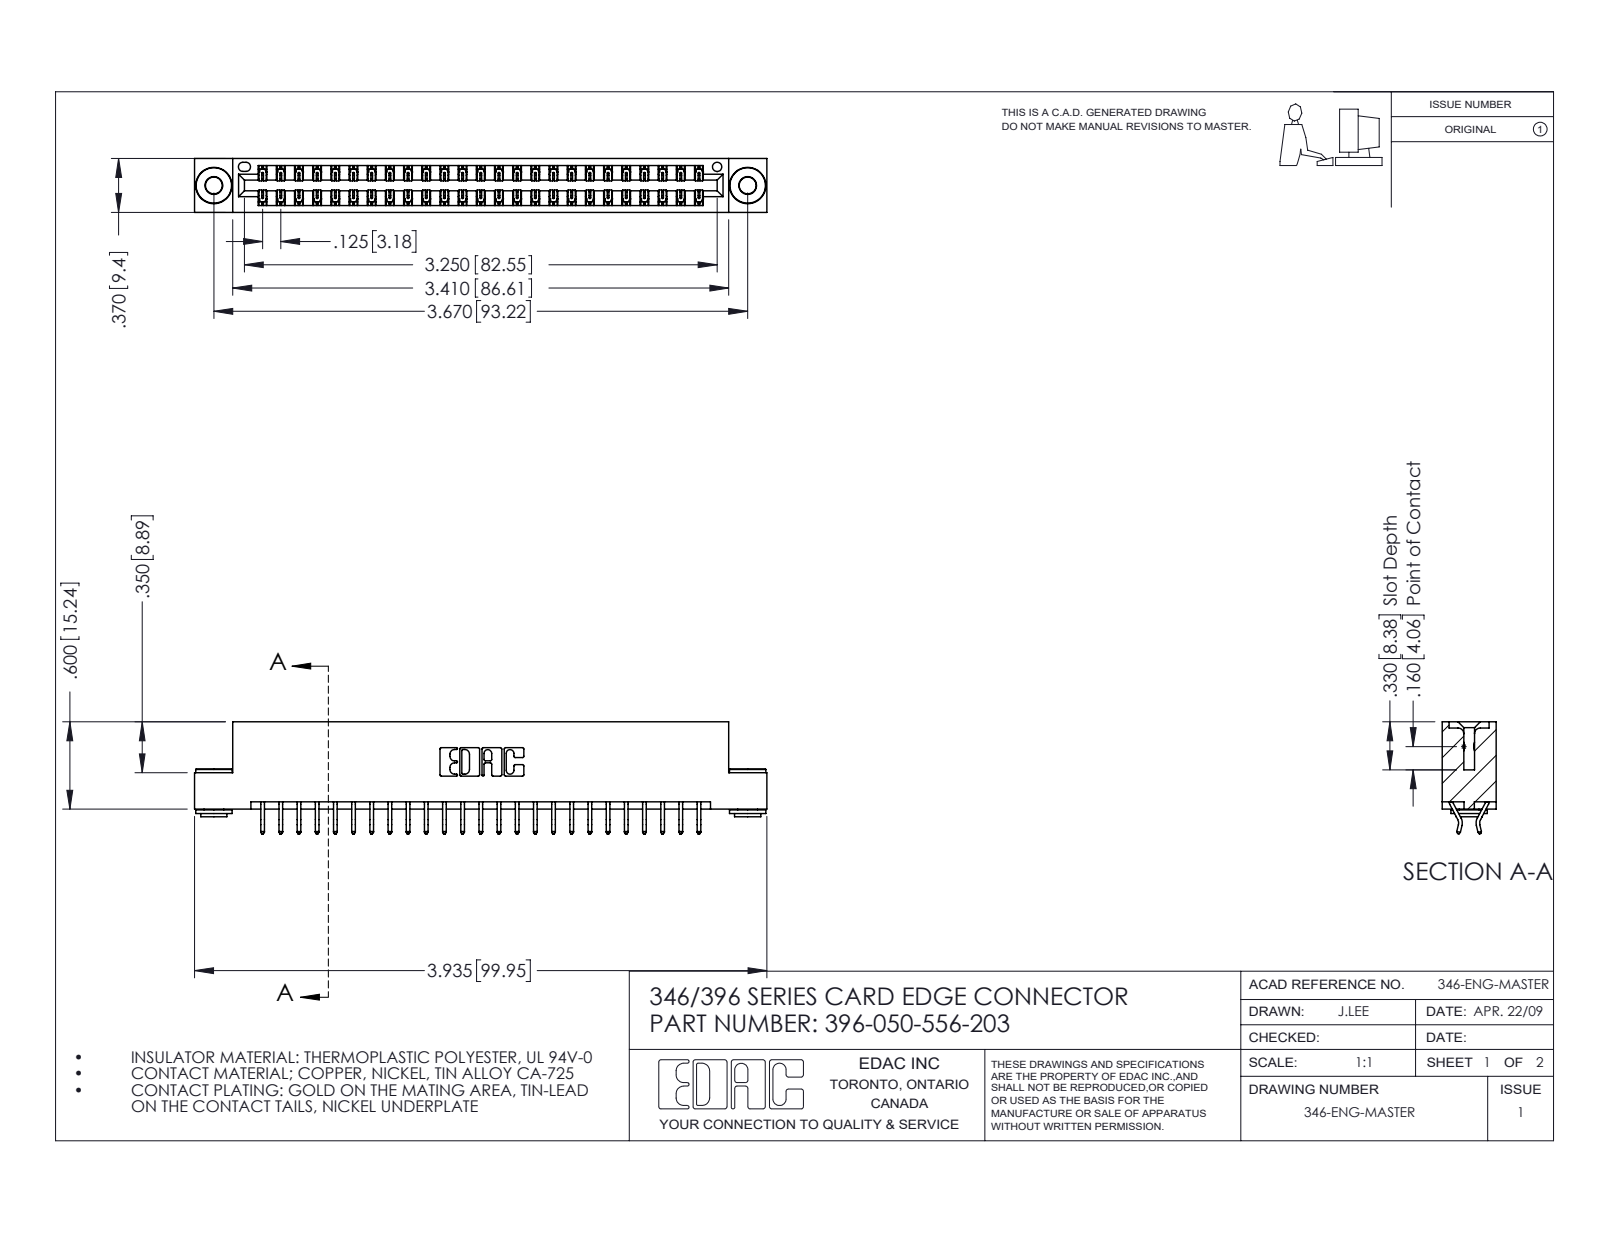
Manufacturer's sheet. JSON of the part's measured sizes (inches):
{"part_name": "345-292-001_556 Tail; 345-250-002_345-250-002-102; 346 Part_Flush Mounting Lugs - 0.156 Dia-TH; 396-050-556-203", "step_written_by": "SolidWorks 2016 (CONFIG_CONTROL_DESIGN)", "units": "inches", "bodies": {"solids": 53, "faces": 3060, "planar": 2036, "cylindrical": 1016, "other": 8}, "overall_size": [3.935, 0.77, 0.37], "volume_in3": 0.588, "surface_area_in2": 20.37, "round_holes": [[0.116, 2], [0.156, 2], [0.064, 1]], "round_bosses_or_shafts": [[0.25, 2], [0.18, 2], [0.136, 2]], "partial_cylinders_radius": [[0.006, 75], [0.01, 22], [0.007, 6], [0.031, 6], [0.026, 3], [0.01, 2], [0.014, 2], [0.022, 2]], "face_to_face_distances": [0.048, 0.322, 0.25, 0.37, 0.025, 0.072, 0.298, 0.275, 0.148, 0.222], "hole_center_spacings": [0.246, 3.462, 3.67]}
